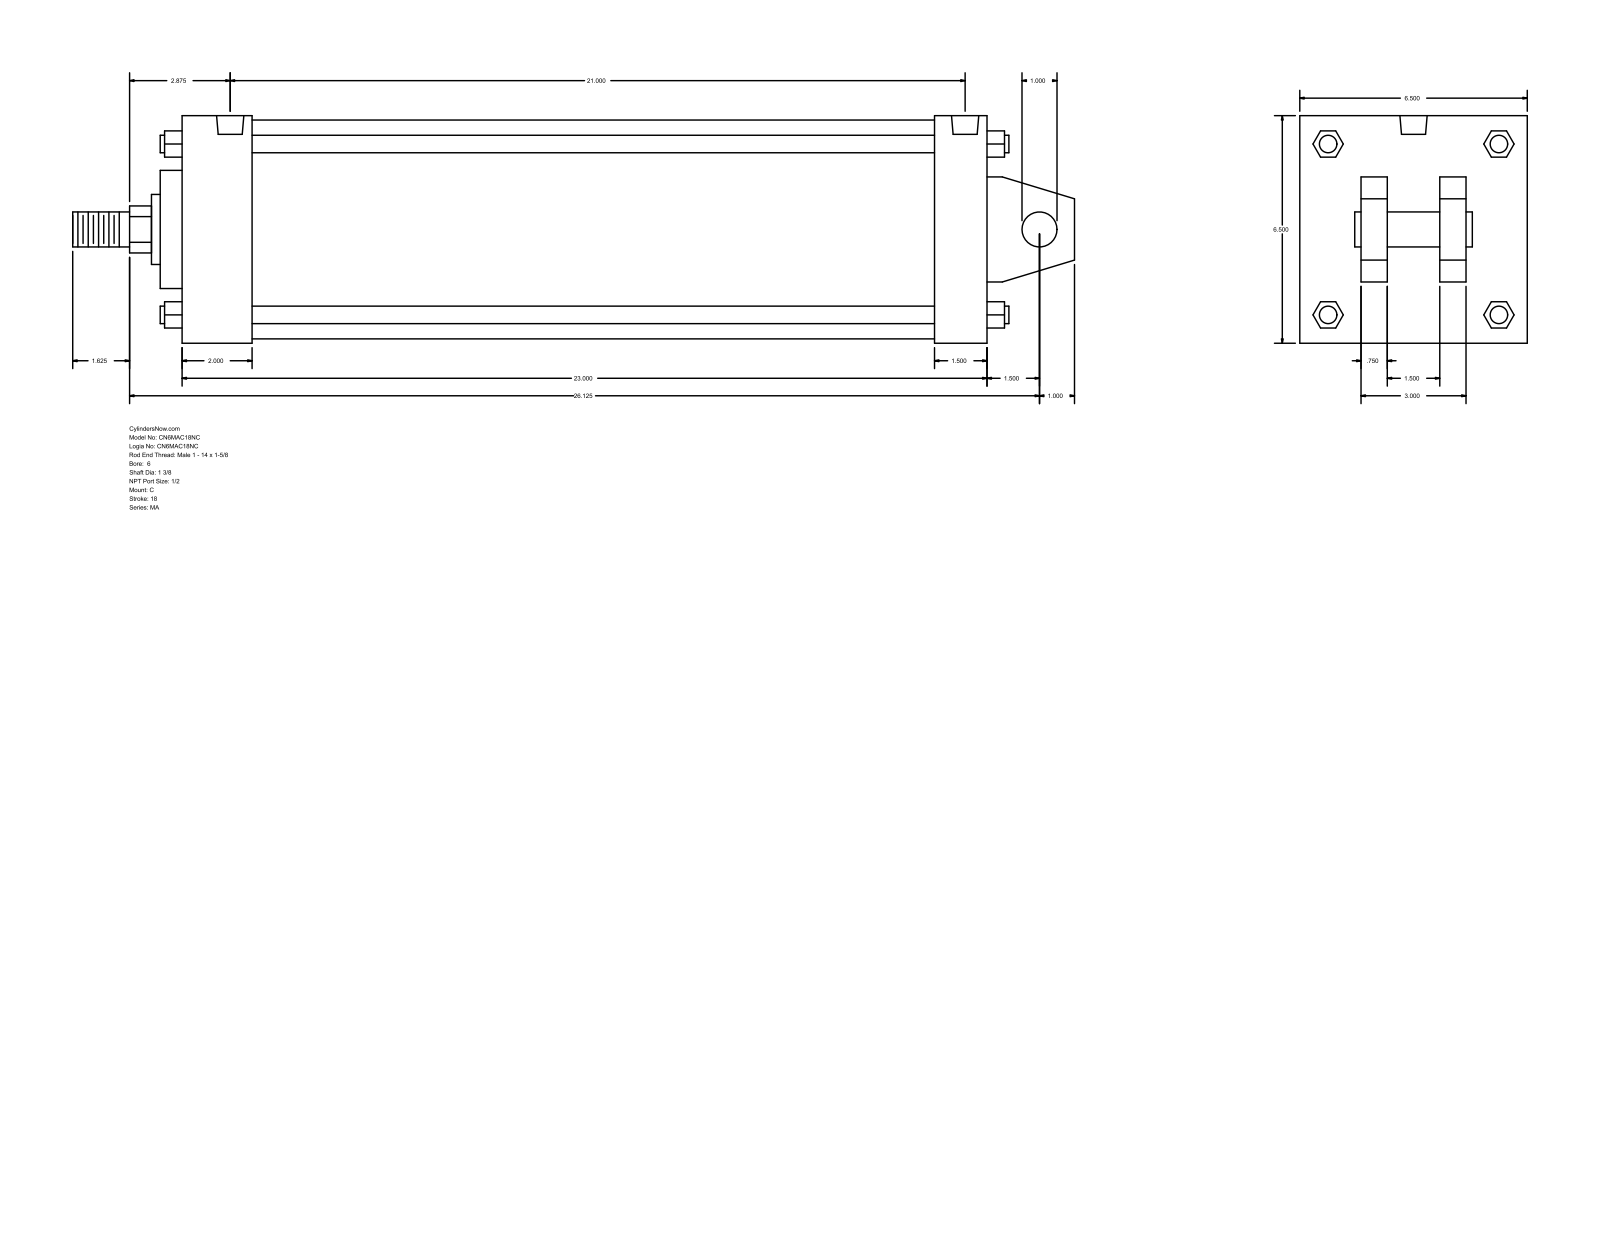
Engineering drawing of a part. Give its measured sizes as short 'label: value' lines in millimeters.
name: MA_C__0600_1.375
written by: GSSL Pune (CONFIG_CONTROL_DESIGN)
unit: mm
bodies: 0 solids, 141 faces (109 planar, 32 cylindrical, 0 other)
size: 727.08 × 165.1 × 165.1
holes: 4× ⌀17.46, 2× ⌀19.77
bosses: 4× ⌀12.7, 2× ⌀25.4, 1× ⌀158.75, 1× ⌀85.72, 1× ⌀50.8, 1× ⌀34.92
rounds: 1× R17.06
face distances: 165.1, 584.2, 38.1, 19.05, 63.5, 101.6, 50.8, 44.45, 120.65, 546.1
hole spacings: 533.4, 3.17, 3.18, 530.22, 533.39, 536.57
